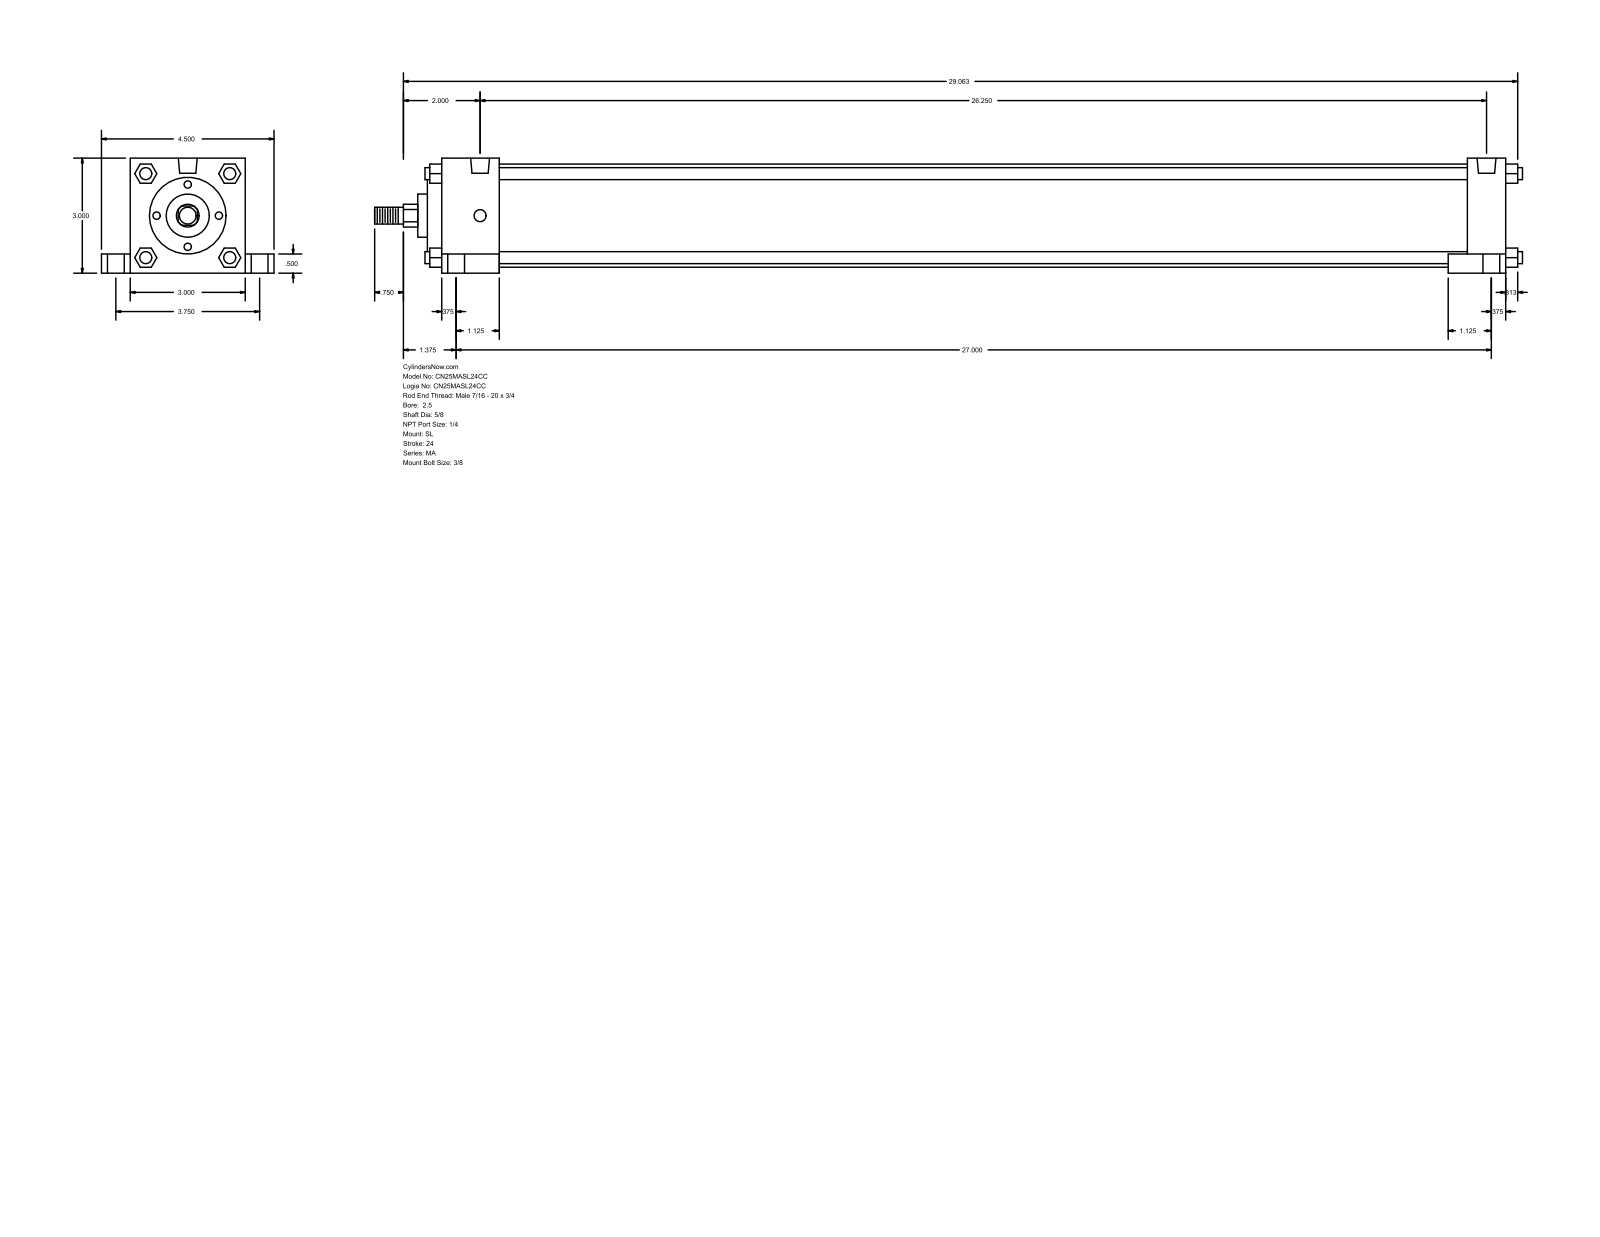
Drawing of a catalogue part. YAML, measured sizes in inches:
part_name: "MA_SL__0250_0.625"
step_written_by: "GSSL Pune (CONFIG_CONTROL_DESIGN)"
units: inches
bodies: {solids: 0, faces: 150, planar: 113, cylindrical: 37, other: 0}
overall_size: [29.937, 4.5, 3]
round_holes:
  - {diameter: 0.313, count: 4}
  - {diameter: 0.437, count: 4}
  - {diameter: 0.687, count: 4}
  - {diameter: 0.492, count: 2}
round_bosses_or_shafts:
  - {diameter: 0.313, count: 4}
  - {diameter: 2.69, count: 1}
  - {diameter: 2, count: 1}
  - {diameter: 1.125, count: 1}
  - {diameter: 0.625, count: 1}
  - {diameter: 0.437, count: 1}
partial_cylinders:
  - {radius: 0.297, count: 1}
face_to_face_distances: [3, 27.75, 0.5, 25.25, 1, 1.5, 26.25, 26.75, 0.75, 2.5]
hole_center_spacings: [1.879, 1.976, 3.75, 26.25, 26.442, 26.941, 27, 27.259]
